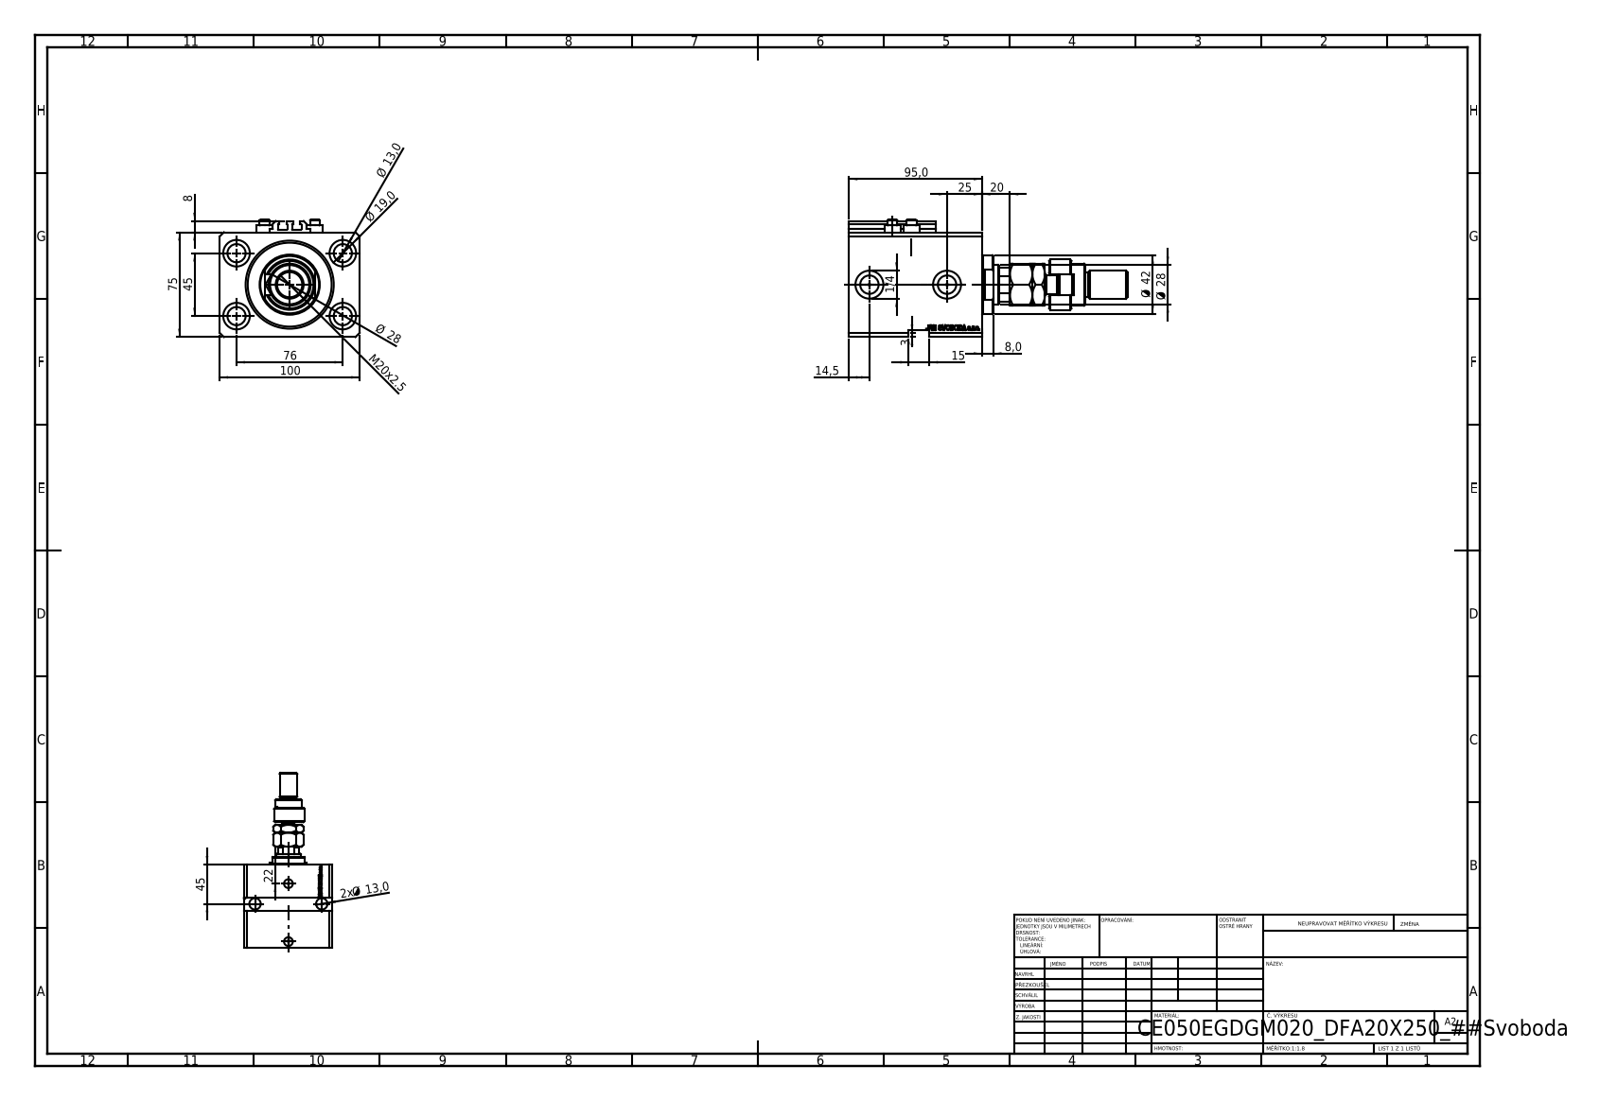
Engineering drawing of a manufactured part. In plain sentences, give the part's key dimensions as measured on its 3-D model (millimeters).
The part is named "FEMALE_PART_FOR_DFA; MFA; V250CE_VC_E; V250CE_C_VCP (+2 more)". Its 3-D file was written by "SolidWorks 2019 (CONFIG_CONTROL_DESIGN)". It is 10 solids with 1189 faces: 567 planar, 151 cylindrical and 471 other. Overall it measures 199 by 100 by 84 millimeters. Its volume is 656 268 cubic millimeters and its surface area 136 312 square millimeters. Round holes: 6 of diameter 13, 4 of diameter 1.25, 4 of diameter 4, 4 of diameter 19, 2 of diameter 10, 2 of diameter 13.16, 2 of diameter 20, 1 of diameter 18.5, 1 of diameter 28, 1 of diameter 50, 1 of diameter 63. Round bosses or shafts: 4 of diameter 11.6, 4 of diameter 7, 1 of diameter 42, 1 of diameter 36, 1 of diameter 30, 1 of diameter 22, 1 of diameter 20, 1 of diameter 18. Partial cylindrical surfaces (rounded edges, fillets, slot ends): 10 of radius 0.2, 1 of radius 7.5, 1 of radius 12, 1 of radius 13.5. The main face-to-face distances are 75, 20, 100, 95, 11.9, 83.1, 63.1, 40, 30, 57.5. The hole center spacings are 44.16, 76, 13.6, 20.72, 27.59, 29.58, 30, 33.62.
